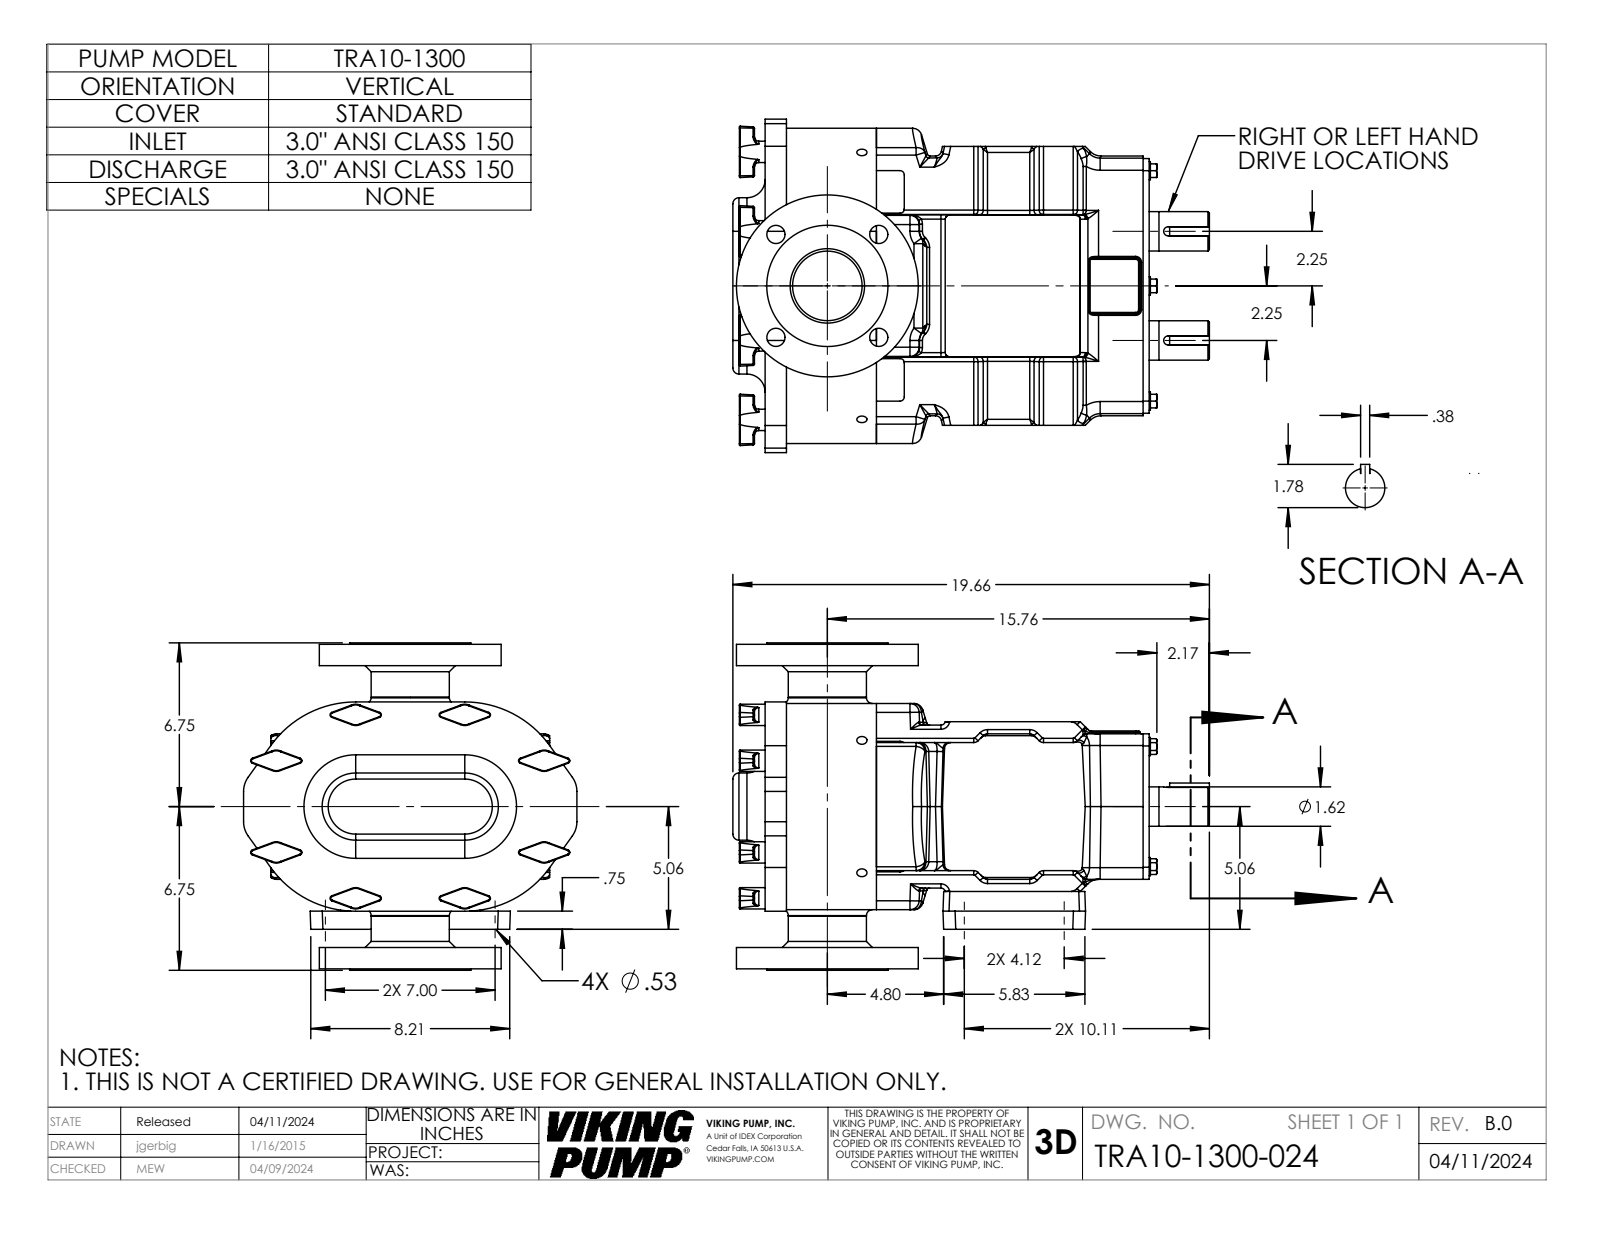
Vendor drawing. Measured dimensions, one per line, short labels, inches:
name: TRA10-1300-BODY; 1300FLG150-30; TRA10-1300-024; TRA10-0600-COVER-STD (+1 more)
written by: SolidWorks 2022 (AUTOMOTIVE_DESIGN)
unit: in
bodies: 5 solids, 1085 faces (285 planar, 404 cylindrical, 396 other)
size: 19.656 × 13.75 × 13.5
volume: 1 341 in³; area: 1 602 in²
holes: 4× ⌀0.332, 4× ⌀0.531, 4× ⌀0.75, 1× ⌀2.868, 1× ⌀3.07
bosses: 8× ⌀0.88, 6× ⌀0.75, 2× ⌀1.624, 1× ⌀7.5, 1× ⌀5, 1× ⌀3.224
rounds: 44× R0.18, 43× R0.06, 32× R0.03, 32× R0.25, 28× R0.38, 24× R0.12, 20× R0.5, 12× R0.375
face distances: 3.712, 0.88, 11.25, 4.592, 15.842, 14.962, 2.81, 8.81, 2.44, 3.17
hole spacings: 3, 2.895, 3.789, 4.12, 4.243, 4.243, 6, 6.637
